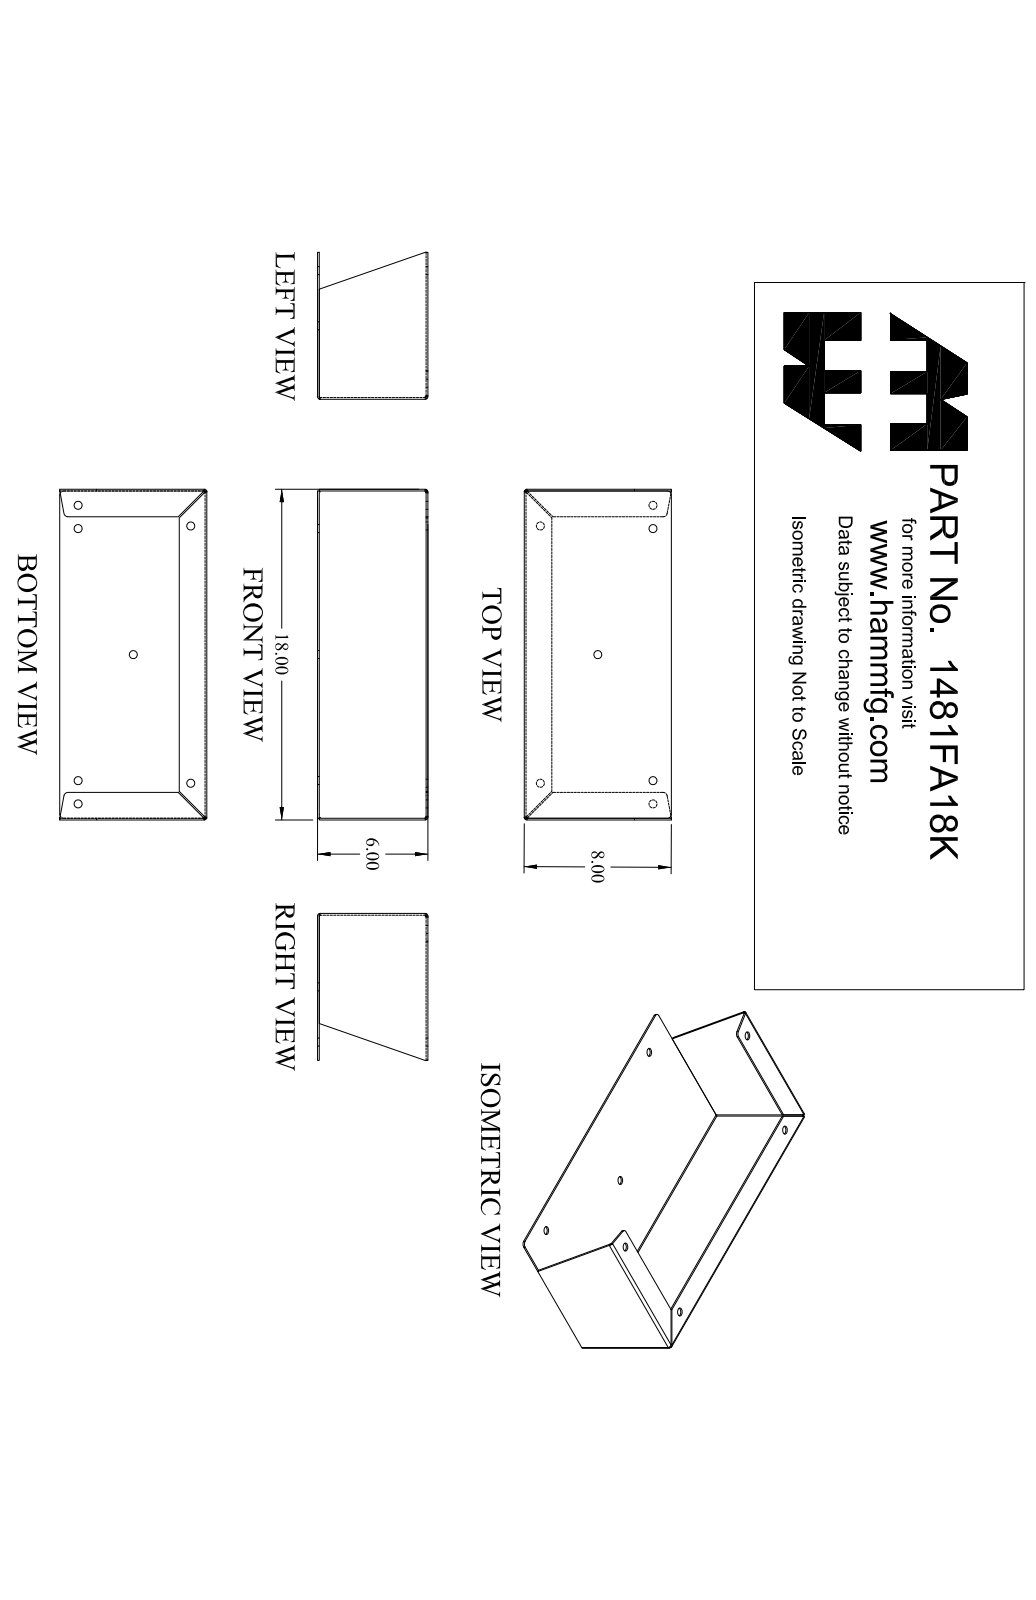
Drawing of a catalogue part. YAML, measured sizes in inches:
part_name: "1481FA18K_Default"
step_written_by: "SolidWorks 2019 (CONFIG_CONTROL_DESIGN)"
units: inches
bodies: {solids: 1, faces: 78, planar: 42, cylindrical: 30, other: 6}
overall_size: [18, 8, 6]
volume: 35.09
surface_area: 748.9
round_holes:
  - {diameter: 0.437, count: 7}
partial_cylinders:
  - {radius: 0.048, count: 6}
  - {radius: 0.143, count: 6}
  - {radius: 0.22, count: 4}
face_to_face_distances: [0.095, 0.095, 17.905, 5.81, 5.905, 5.905, 6, 18, 17.81, 1.5]
hole_center_spacings: [6.126, 6.227, 7.487, 7.666, 15.152, 1.266, 1.266, 8.661]
